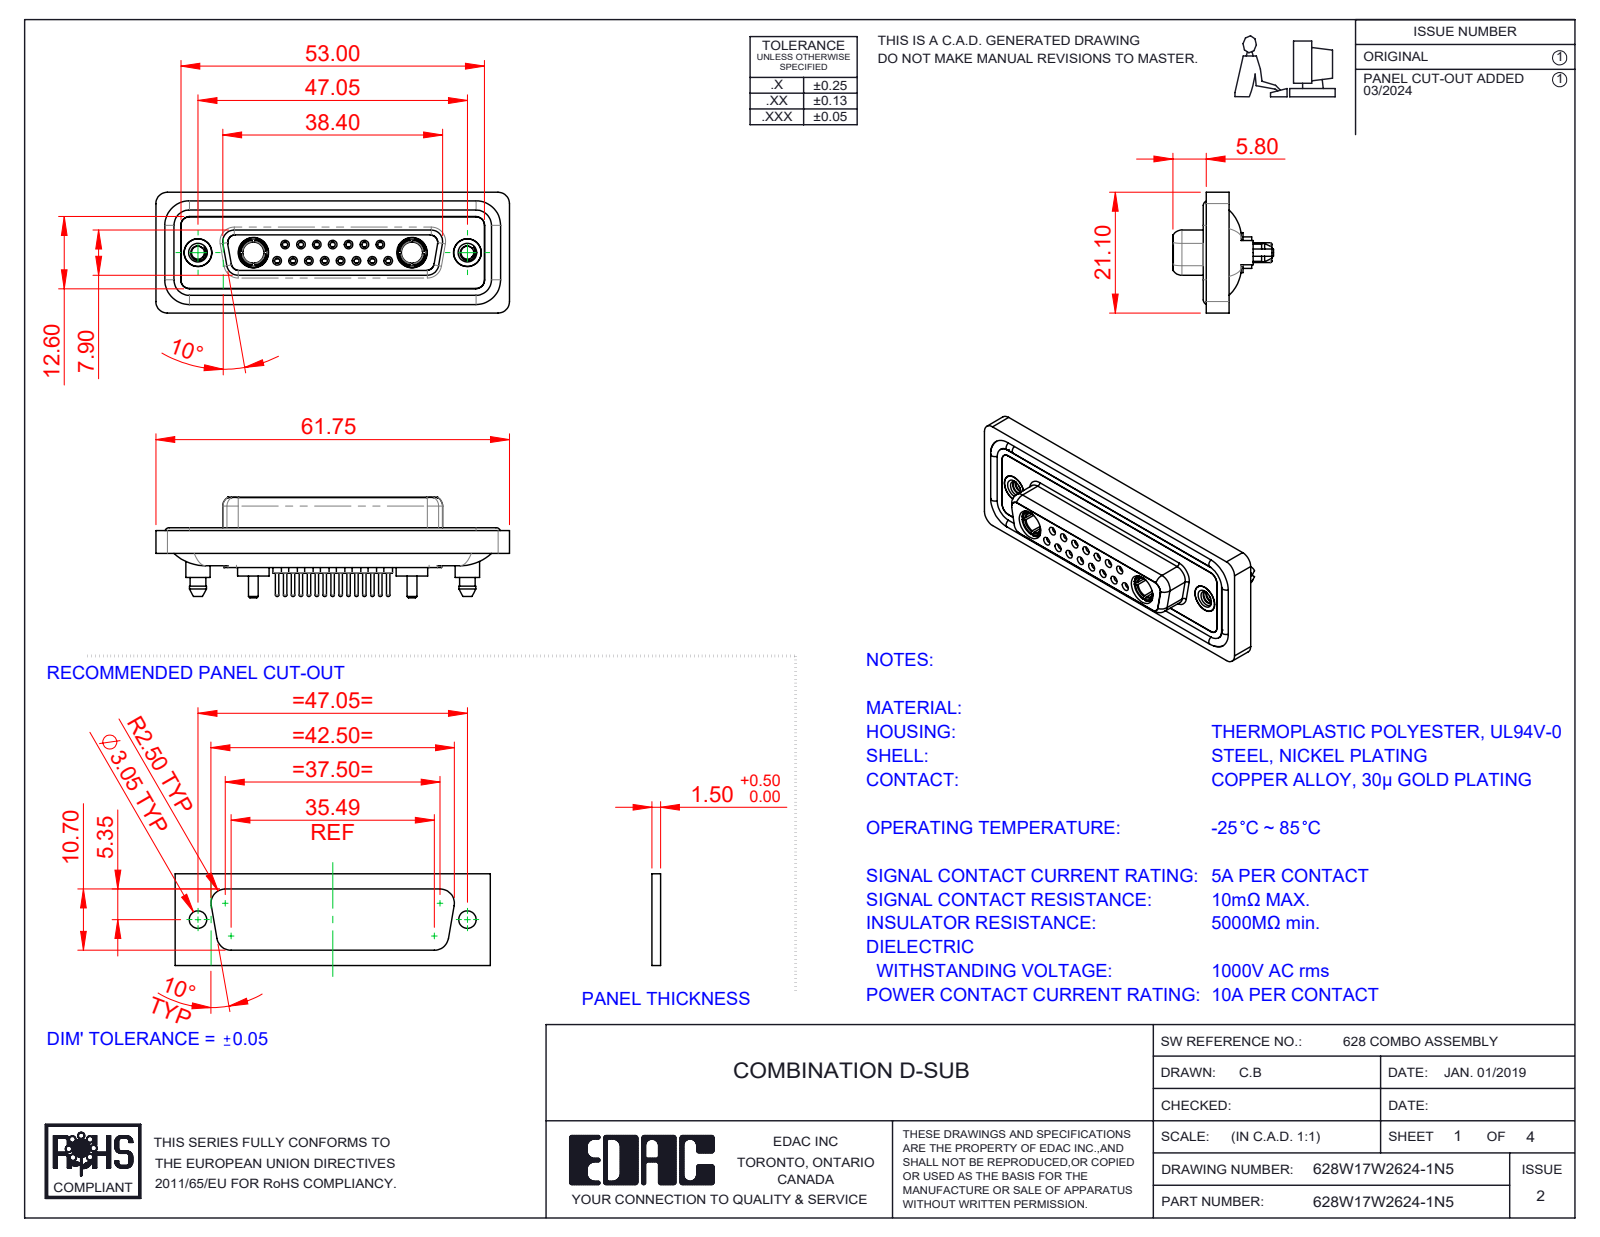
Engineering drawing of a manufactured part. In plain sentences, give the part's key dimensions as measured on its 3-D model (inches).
The part is named "Power Socket_10A S; 628Combo Waterproof Housing_25 Contacts; 628Combo Shell Rear_25 Contacts; 628W17W2624-1N5 (+5 more)". Its 3-D file was written by "SolidWorks 2023 (CONFIG_CONTROL_DESIGN)". It is 26 solids with 1409 faces: 404 planar, 551 cylindrical and 454 other. Overall it measures 2.431 by 0.831 by 0.691 inches. Its volume is 0.514 cubic inches and its surface area 21.95 square inches. Round holes: 15 of diameter 0.035, 15 of diameter 0.043, 15 of diameter 0.059, 15 of diameter 0.079, 8 of diameter 0.063, 7 of diameter 0.067, 4 of diameter 0.191, 2 of diameter 0.089, 2 of diameter 0.146, 2 of diameter 0.157, 2 of diameter 0.159, 2 of diameter 0.197. Round bosses or shafts: 15 of diameter 0.087, 15 of diameter 0.024, 11 of diameter 0.063, 2 of diameter 0.217, 2 of diameter 0.213, 2 of diameter 0.205, 2 of diameter 0.195, 2 of diameter 0.195. Partial cylindrical surfaces (rounded edges, fillets, slot ends): 24 of radius 0.059, 18 of radius 0.079, 10 of radius 0.063, 8 of radius 0.053, 4 of radius 0.01, 4 of radius 0.02, 4 of radius 0.024, 4 of radius 0.026. The main face-to-face distances are 0.016, 0.071, 0.293, 0.222, 0.26, 0.02, 0.278, 0.063, 0.114, 0.043. The hole center spacings are 0.124, 0.109, 0.327, 0.218, 0.198, 0.198, 0.295, 0.436.
